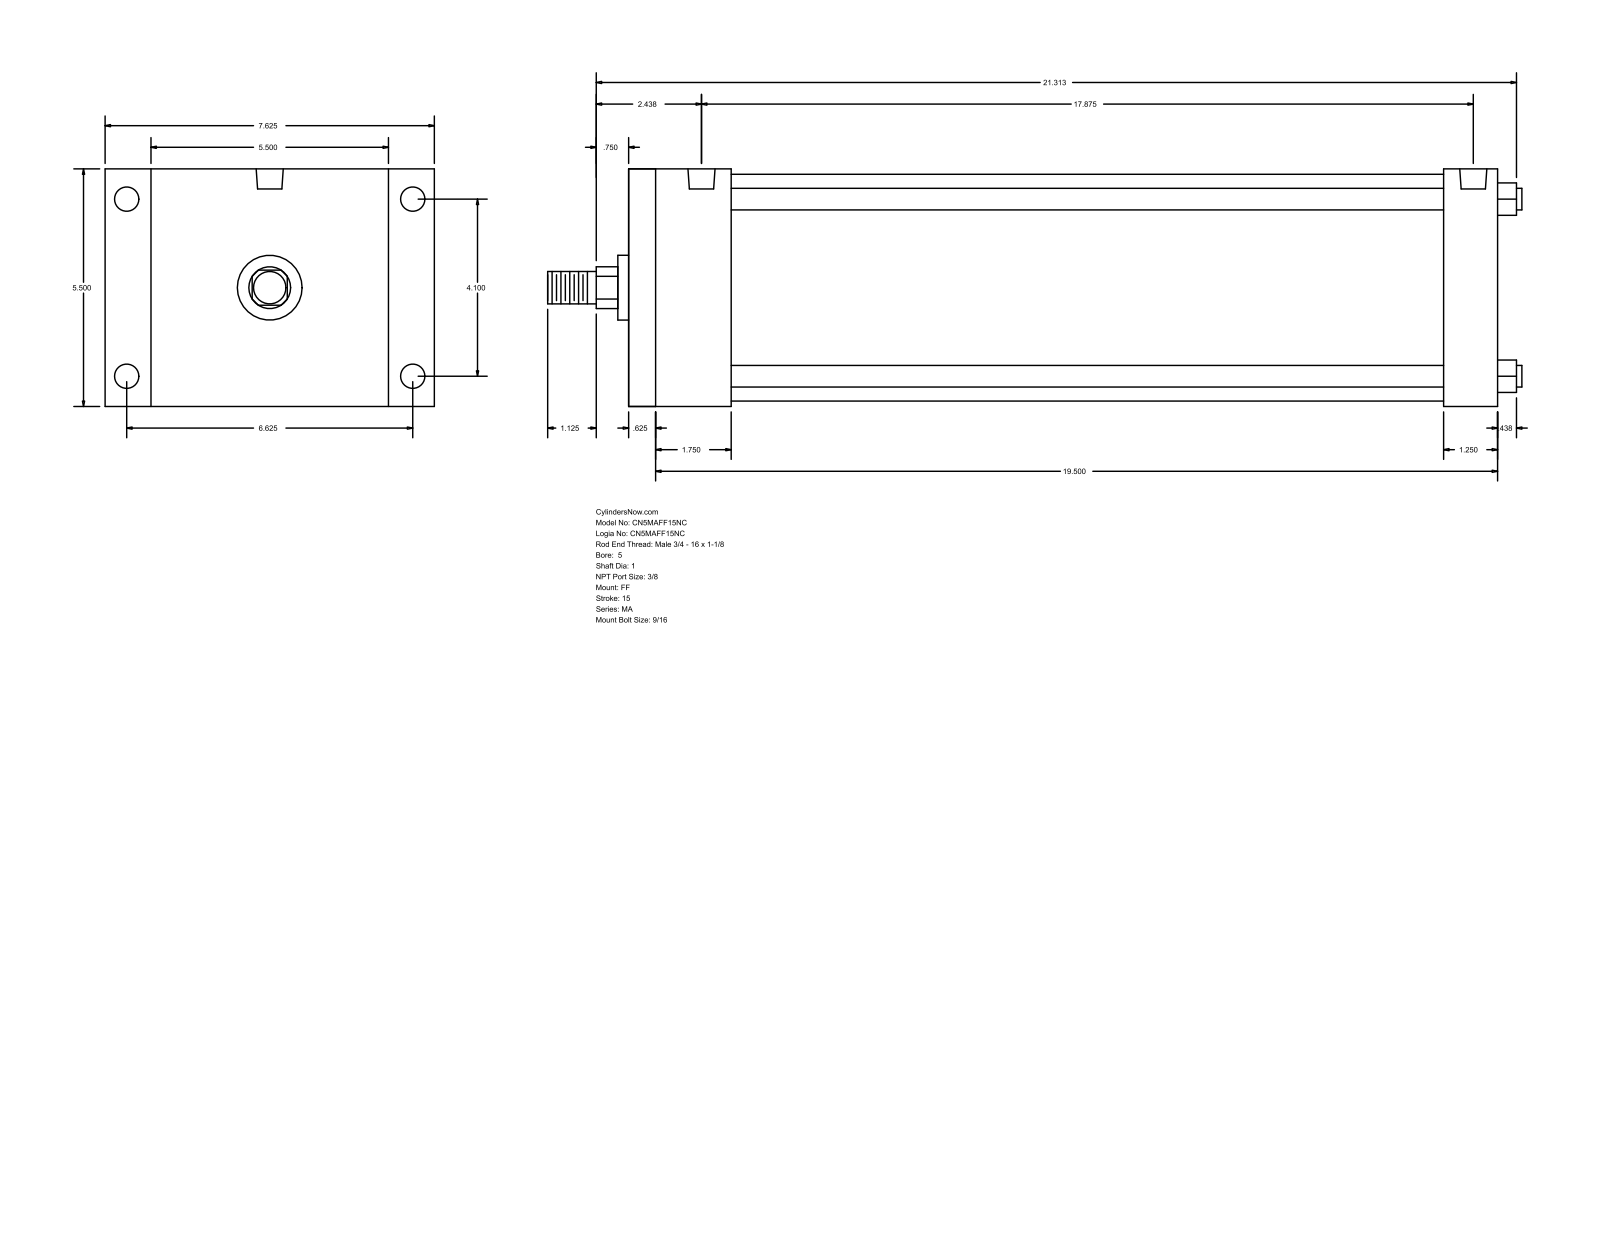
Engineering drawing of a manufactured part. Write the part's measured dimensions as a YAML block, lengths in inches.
part_name: "MA_FF__0500_1"
step_written_by: "GSSL Pune (CONFIG_CONTROL_DESIGN)"
units: inches
bodies: {solids: 0, faces: 92, planar: 64, cylindrical: 28, other: 0}
overall_size: [22.563, 7.625, 5.5]
round_holes:
  - {diameter: 0.437, count: 4}
  - {diameter: 0.563, count: 4}
  - {diameter: 0.627, count: 2}
round_bosses_or_shafts:
  - {diameter: 0.5, count: 4}
  - {diameter: 5.25, count: 1}
  - {diameter: 1.5, count: 1}
  - {diameter: 1, count: 1}
  - {diameter: 0.75, count: 1}
partial_cylinders:
  - {radius: 0.484, count: 1}
face_to_face_distances: [5.5, 20.125, 0.625, 19.5, 18.875, 18.25, 1.25, 2.375, 1.75, 16.5]
hole_center_spacings: [0.187, 4.1, 6.625, 7.791, 17.5, 17.688, 17.875]
